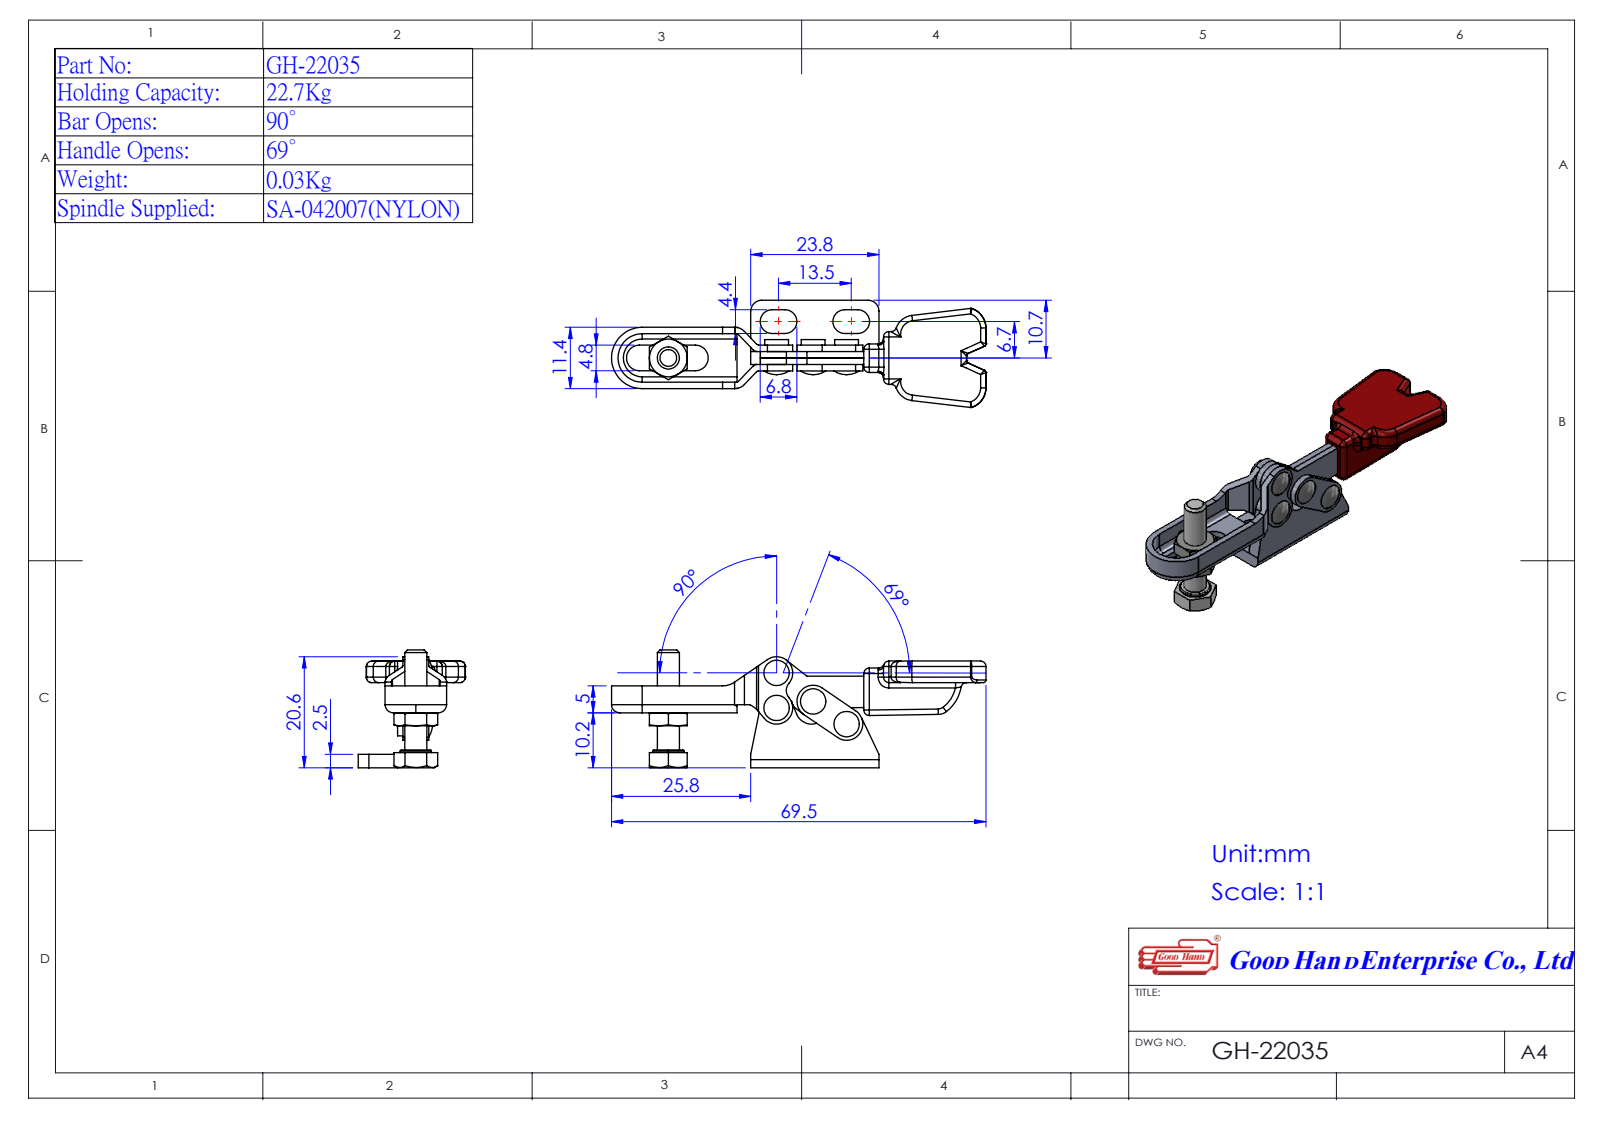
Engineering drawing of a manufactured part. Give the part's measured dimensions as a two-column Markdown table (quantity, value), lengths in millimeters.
| quantity | value |
| --- | --- |
| part name | 12202013(簡化); Group3^GH-22035(簡化); GH-22035(簡化); Group5^GH-22035(簡化) (+2 more) |
| STEP written by | SolidWorks 2016 (AUTOMOTIVE_DESIGN) |
| units | millimeters |
| bodies | 5 solids, 278 faces (117 planar, 113 cylindrical, 48 other) |
| overall size | 69.5 × 23.3 × 19.89 |
| volume | 4 504 mm³ |
| surface area | 5 283 mm² |
| round holes (diameter × count) | 2 × 4 |
| round bosses / shafts (diameter × count) | 3.5 × 4, 6 × 1, 5.8 × 1, 4.1 × 1 |
| partial cylindrical surfaces (radius × count) | 1 × 20, 0.5 × 5, 3 × 5, 2 × 4, 2.2 × 4, 2.5 × 3, 2.38 × 2, 3.5 × 2 |
| main face-to-face distances | 1.2, 2.4, 10.2, 4.5, 6.9, 3.3, 5.7, 19.8, 8.4, 11.4 |
| hole center spacings | 6.5, 6.91, 7.49, 8.62, 13.34, 16.1 |
